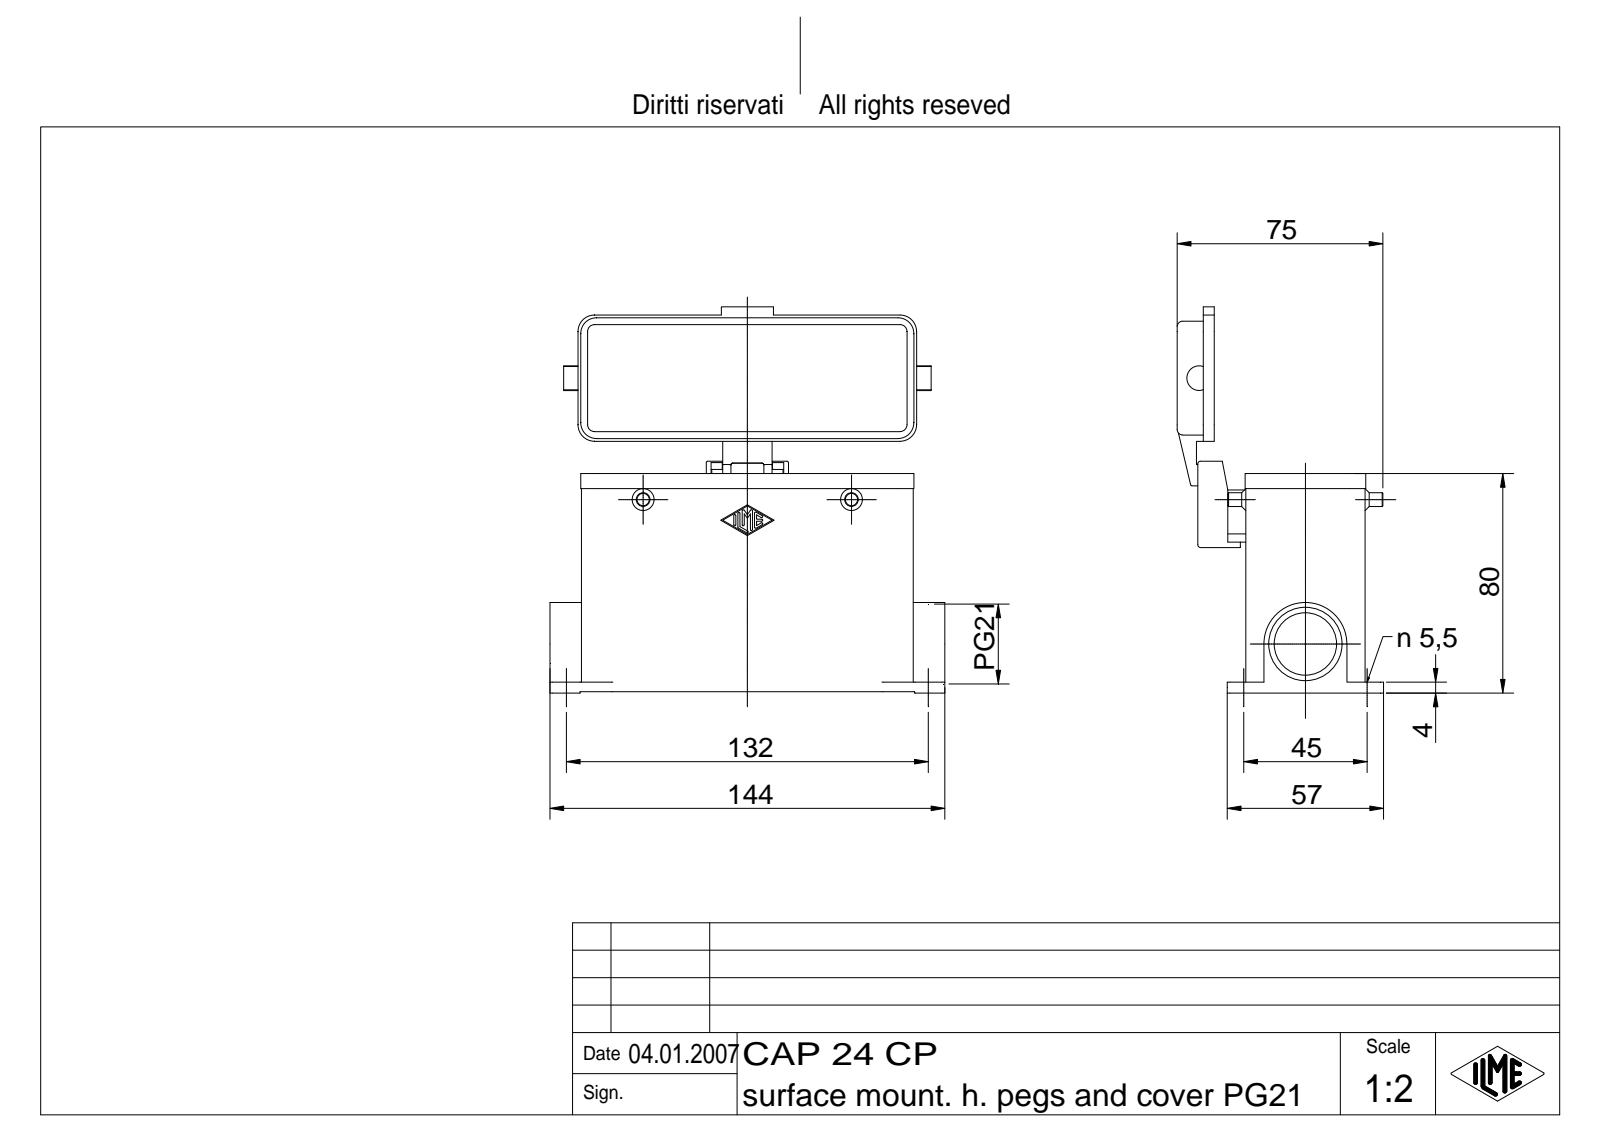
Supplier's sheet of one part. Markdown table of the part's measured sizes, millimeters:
| quantity | value |
| --- | --- |
| part name | CAP 24 CP |
| STEP written by | Autodesk Inventor 7 (AUTOMOTIVE_DESIGN) |
| units | millimeters |
| bodies | 1 solid, 470 faces (195 planar, 164 cylindrical, 111 other) |
| overall size | 144 × 140.75 × 75.25 |
| volume | 153 981 mm³ |
| surface area | 90 679 mm² |
| round holes (diameter × count) | 5.5 × 4, 4 × 1, 5 × 1, 22.78 × 1, 26.78 × 1 |
| round bosses / shafts (diameter × count) | 5 × 2, 3 × 2, 7 × 1, 4 × 1 |
| partial cylindrical surfaces (radius × count) | 0.38 × 14, 1 × 14, 6 × 12, 0.5 × 10, 0.7 × 8, 2 × 8, 2.5 × 4, 3 × 4 |
| main face-to-face distances | 3, 40.5, 43.5, 37.5, 2.5, 3.5, 22.5, 63, 68.5, 66 |
| hole center spacings | 45, 132, 139.46 |
